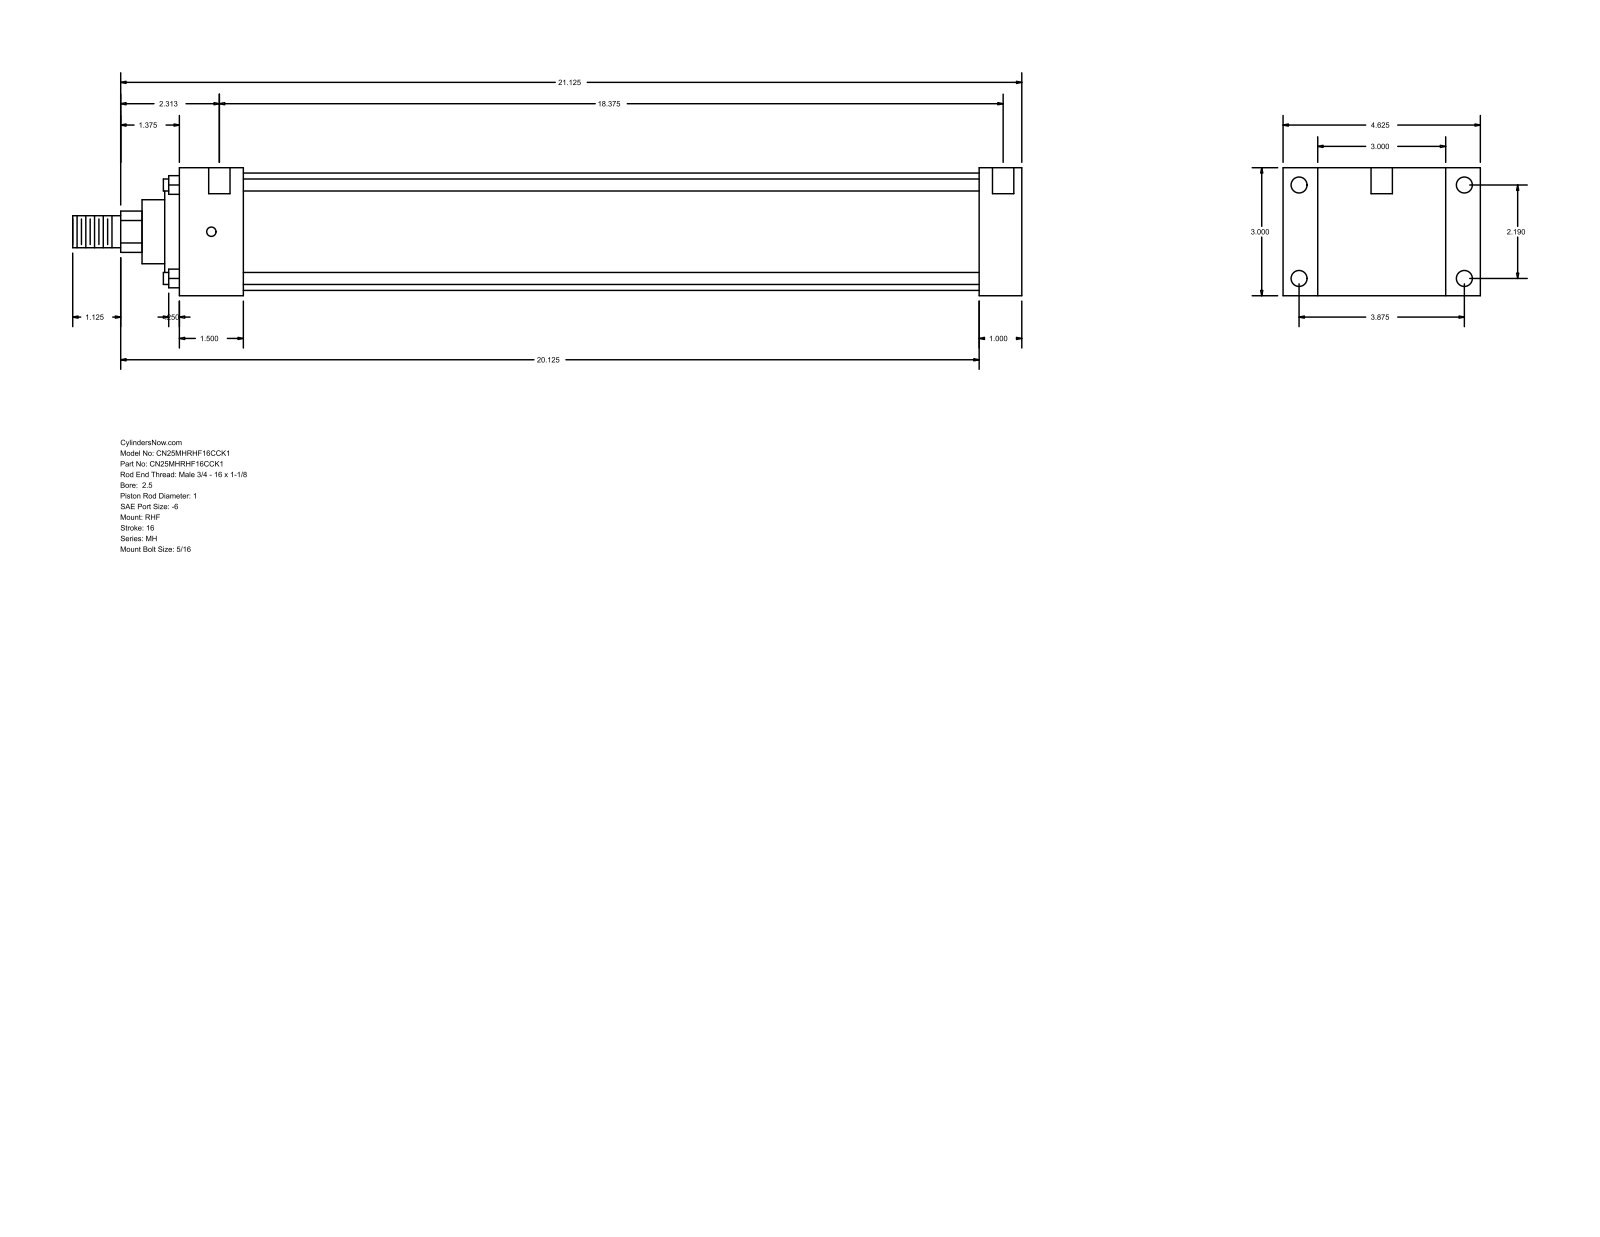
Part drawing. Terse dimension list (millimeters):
name: MH_RHF__0250_1
written by: GSSL Pune (CONFIG_CONTROL_DESIGN)
unit: mm
bodies: 0 solids, 90 faces (61 planar, 29 cylindrical, 0 other)
size: 565.15 × 117.47 × 76.2
holes: 4× ⌀5.56, 4× ⌀9.53, 2× ⌀12.7
bosses: 4× ⌀7.14, 1× ⌀69.85, 1× ⌀60.33, 1× ⌀38.1, 1× ⌀25.4, 1× ⌀19.05
rounds: 1× R12.29
face distances: 76.2, 25.4, 20.64, 96.84, 476.26, 501.66, 117.48, 38.11, 438.15, 463.55
hole spacings: 55.62, 98.42, 113.05, 474.66, 3.18, 4.76, 466.72, 469.9
